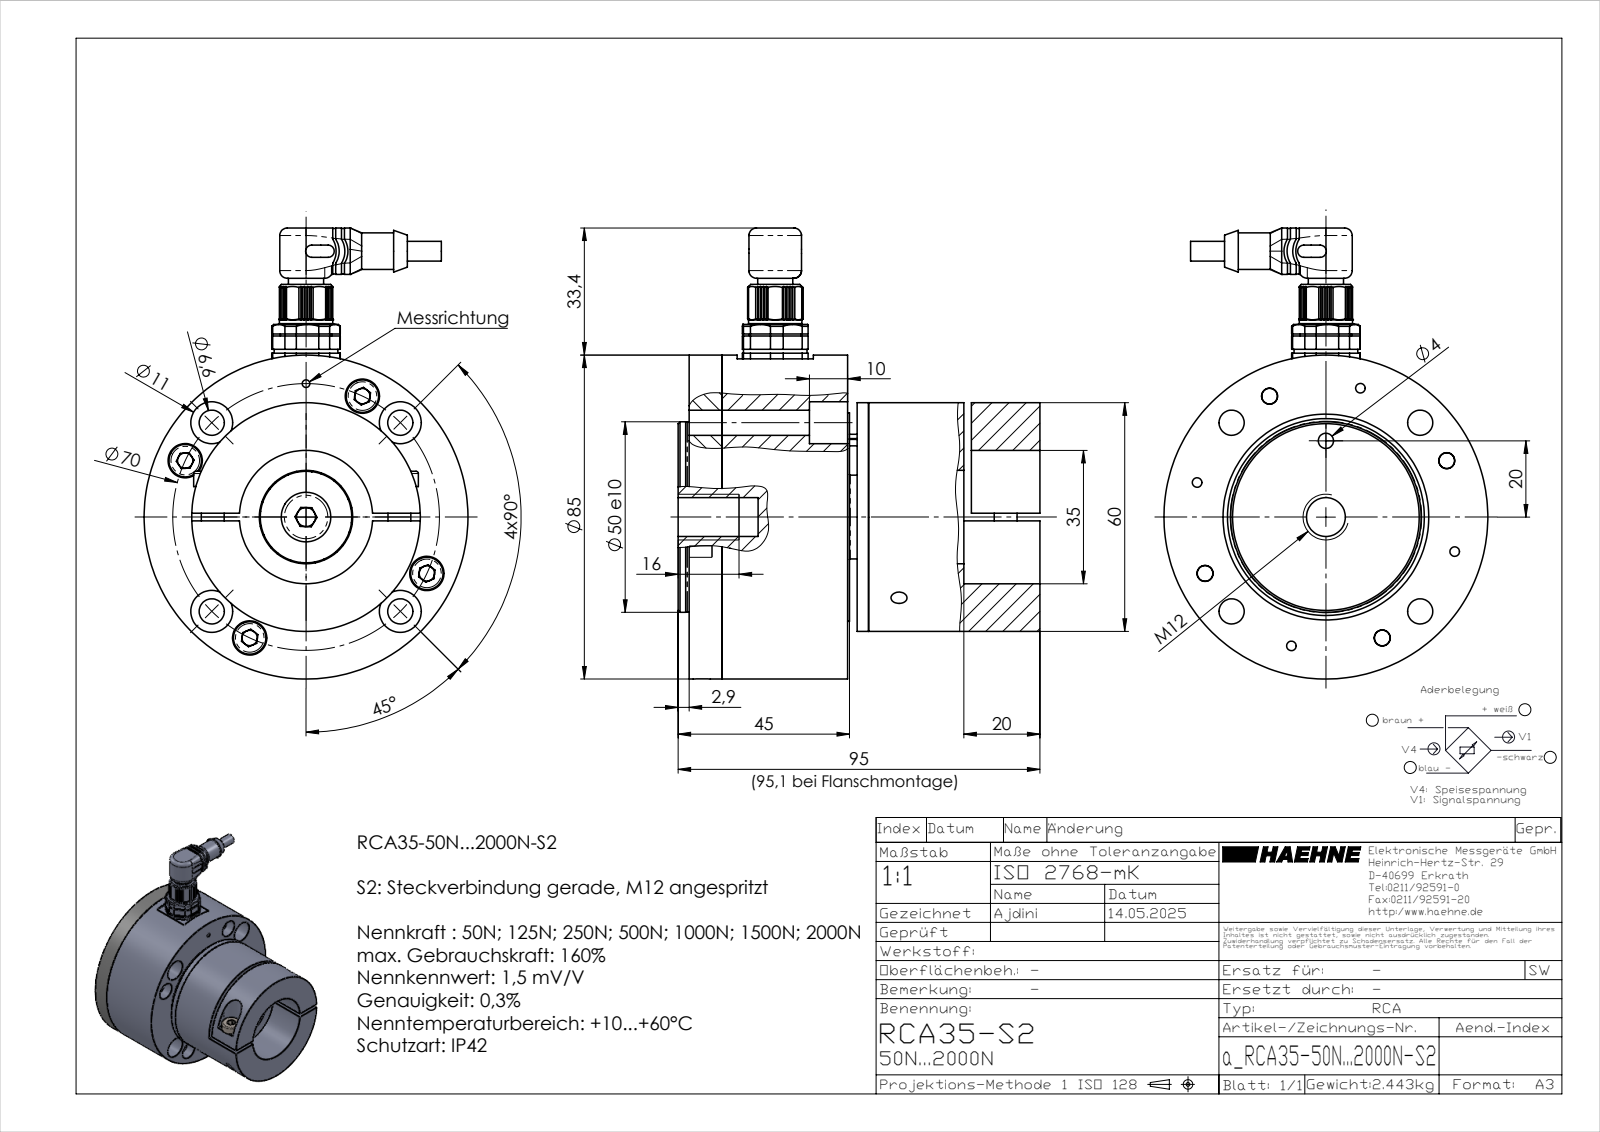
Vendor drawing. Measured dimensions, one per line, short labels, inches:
name: DIN 7991 - M3 x 8 --- 4.8N_DIN 7991 - M3 x 8 --- 4.8N; inafag_1203-tvh_7zkvytp7yxkimpdvw8sj0b5w4_13; DIN 7984 - M8 x 12 --- 8.25N_DIN 7984 - M8 x 12 --- 8.25N; inafag_1203-tvh_7zkvytp7yxkimpdvw8sj0b5w4_07 (+8 more)
written by: SolidWorks 2023 (AUTOMOTIVE_DESIGN)
unit: in
bodies: 53 solids, 1226 faces (662 planar, 295 cylindrical, 269 other)
size: 4.659 × 3.744 × 3.346
volume: 21.81 in³; area: 174.3 in²
holes: 9× ⌀0.134, 8× ⌀0.098, 6× ⌀0.26, 5× ⌀0.165, 5× ⌀0.433, 4× ⌀0.043, 4× ⌀0.045, 4× ⌀0.063, 4× ⌀0.073, 4× ⌀0.157, 4× ⌀0.209, 4× ⌀0.354
bosses: 9× ⌀0.118, 8× ⌀0.224, 4× ⌀0.335, 4× ⌀0.197, 4× ⌀0.071, 4× ⌀0.061, 4× ⌀0.059, 4× ⌀0.039
rounds: 16× R0.008, 9× R0.012, 4× R0.016, 4× R0.021, 4× R0.039, 4× R0.05, 4× R0.236, 2× R0.063
face distances: 0.118, 0.339, 0.079, 1.854, 0.457, 1.181, 1.772, 1.969, 1.398, 1.972
hole spacings: 1.378, 1.949, 0.976, 0.992, 1.291, 2.013, 2.223, 0.098
